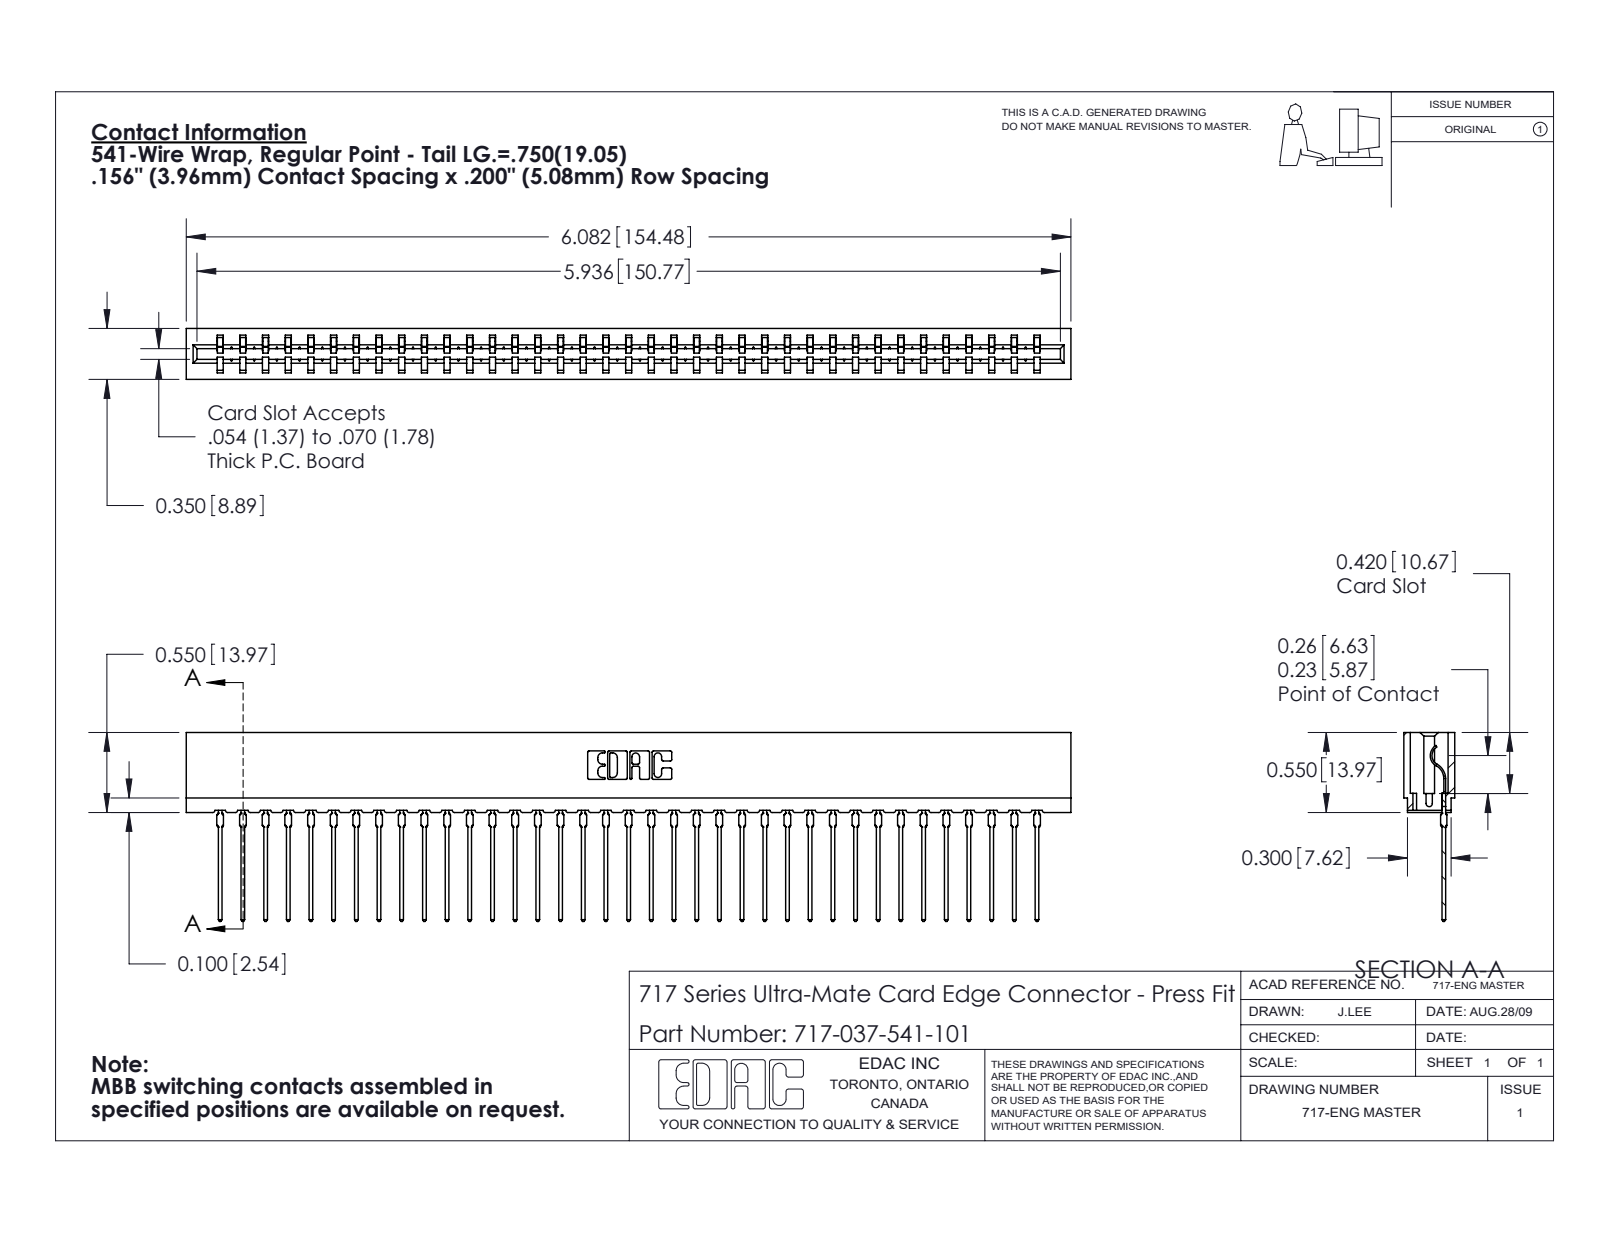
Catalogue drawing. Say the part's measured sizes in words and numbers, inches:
The part is named "717 Part_Insulator Option - 06; 745-292-001_541; 717-037-541-101". Its 3-D file was written by "SolidWorks 2020 (CONFIG_CONTROL_DESIGN)". It is 38 solids with 4275 faces: 2570 planar, 743 cylindrical and 962 other. Overall it measures 6.082 by 1.299 by 0.35 inches. Its volume is 0.807 cubic inches and its surface area 29.92 square inches. Partial cylindrical surfaces (rounded edges, fillets, slot ends): 74 of radius 0.015, 74 of radius 0.021, 22 of radius 0.01, 6 of radius 0.007, 6 of radius 0.031, 4 of radius 0.005, 4 of radius 0.011, 3 of radius 0.026. The main face-to-face distances are 0.212, 0.138, 0.35, 0.063, 0.287, 0.076, 0.149, 0.074, 0.045, 0.305.
